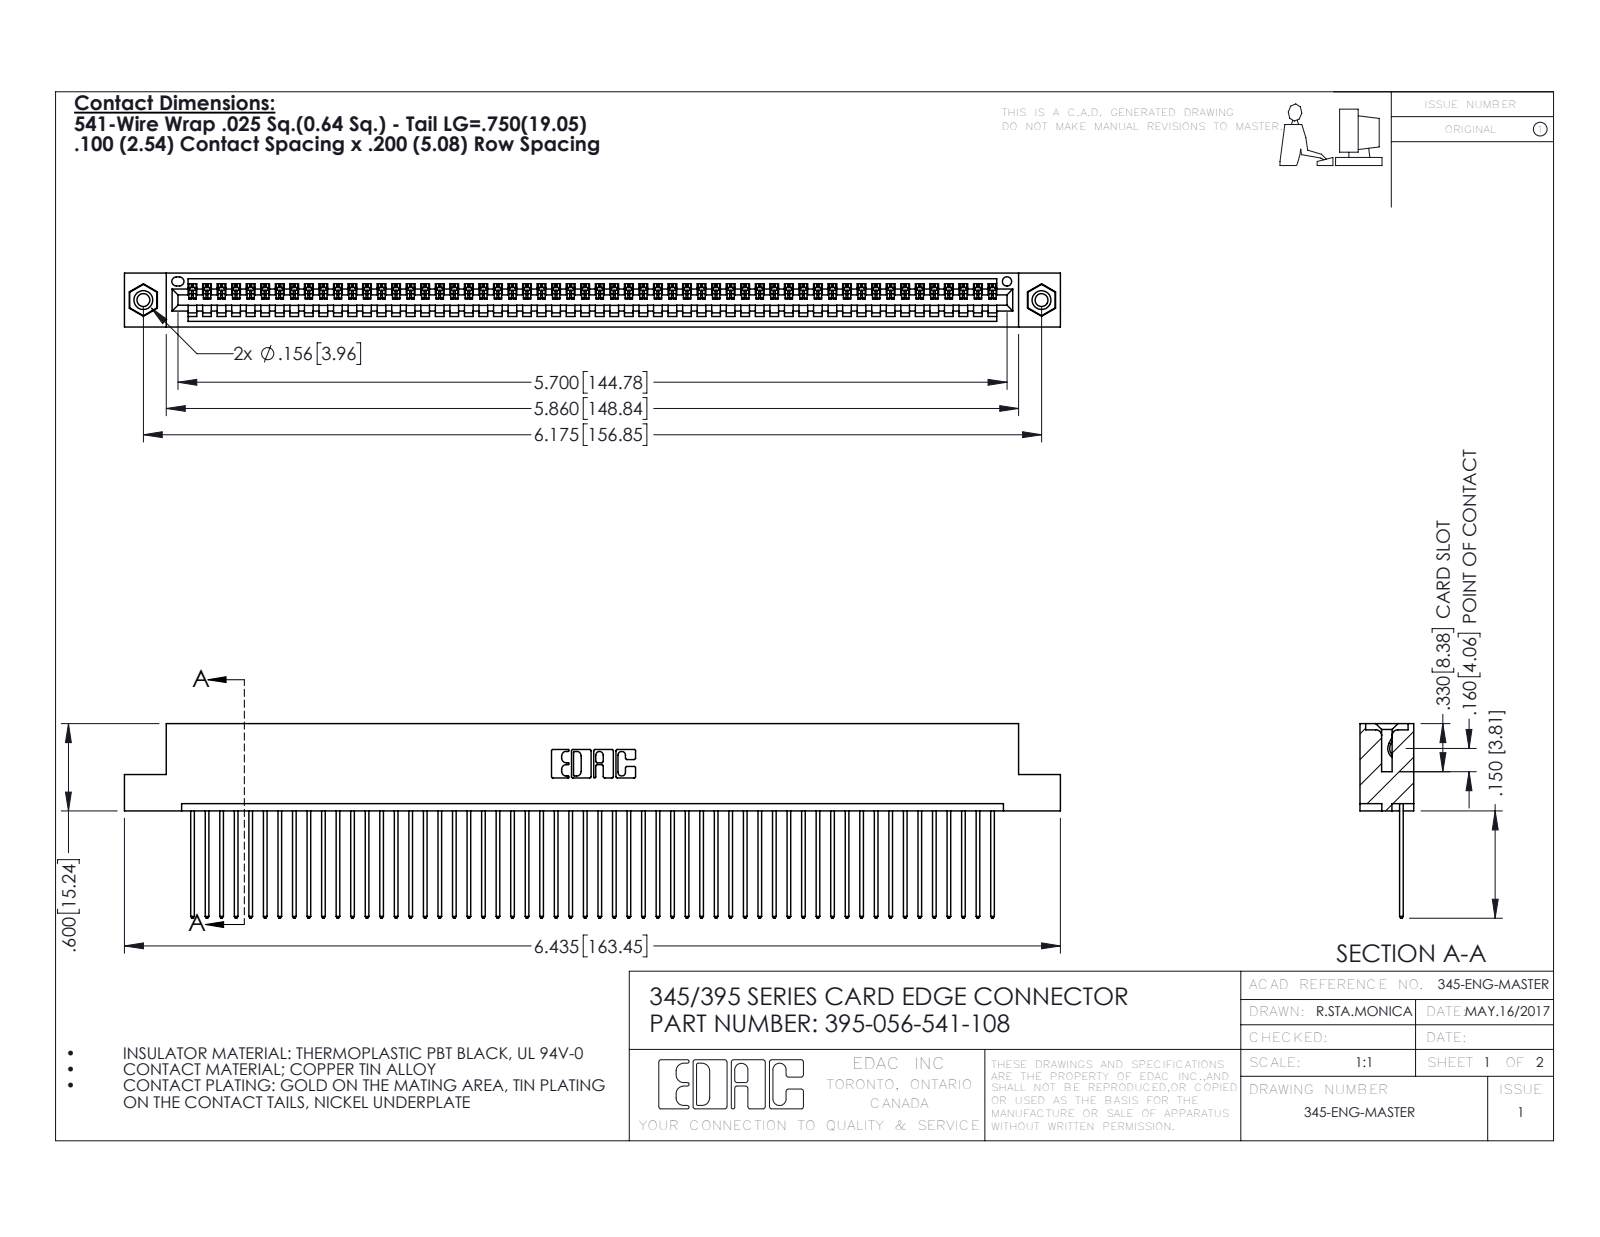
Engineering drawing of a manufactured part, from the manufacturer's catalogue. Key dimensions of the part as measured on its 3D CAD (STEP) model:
Part name (STEP PRODUCT): 345-250-001_345-250-003-102; 345 Part_Flush Mounting Lugs - 0.156 Dia-TI; 345-292-001_345-293-141; 395-056-541-108
STEP written by: SolidWorks 2016 (CONFIG_CONTROL_DESIGN)
Units: inches
Bodies: 59 solids, 3434 faces (2352 planar, 1066 cylindrical, 16 other)
Overall size (bounding box): 6.435 × 1.337 × 0.37
Volume: 0.965 in³ · Surface area: 34.59 in²
Round holes (diameter × count): ⌀0.089 ×2, ⌀0.125 ×2, ⌀0.156 ×2, ⌀0.064 ×1
Round bosses / shafts (diameter × count): ⌀0.155 ×2
Partial cylindrical surfaces — rounded edges, fillets, slot ends (radius × count): R0.006 ×112, R0.01 ×112, R0.01 ×22, R0.007 ×6, R0.031 ×6, R0.026 ×3, R0.031 ×2, R0.04 ×2
Main face-to-face distances: 0.072, 0.298, 0.098, 0.272, 0.025, 0.37, 0.2, 0.225, 0.149, 0.072
Hole centre spacings: 0.27, 5.939, 6.175
